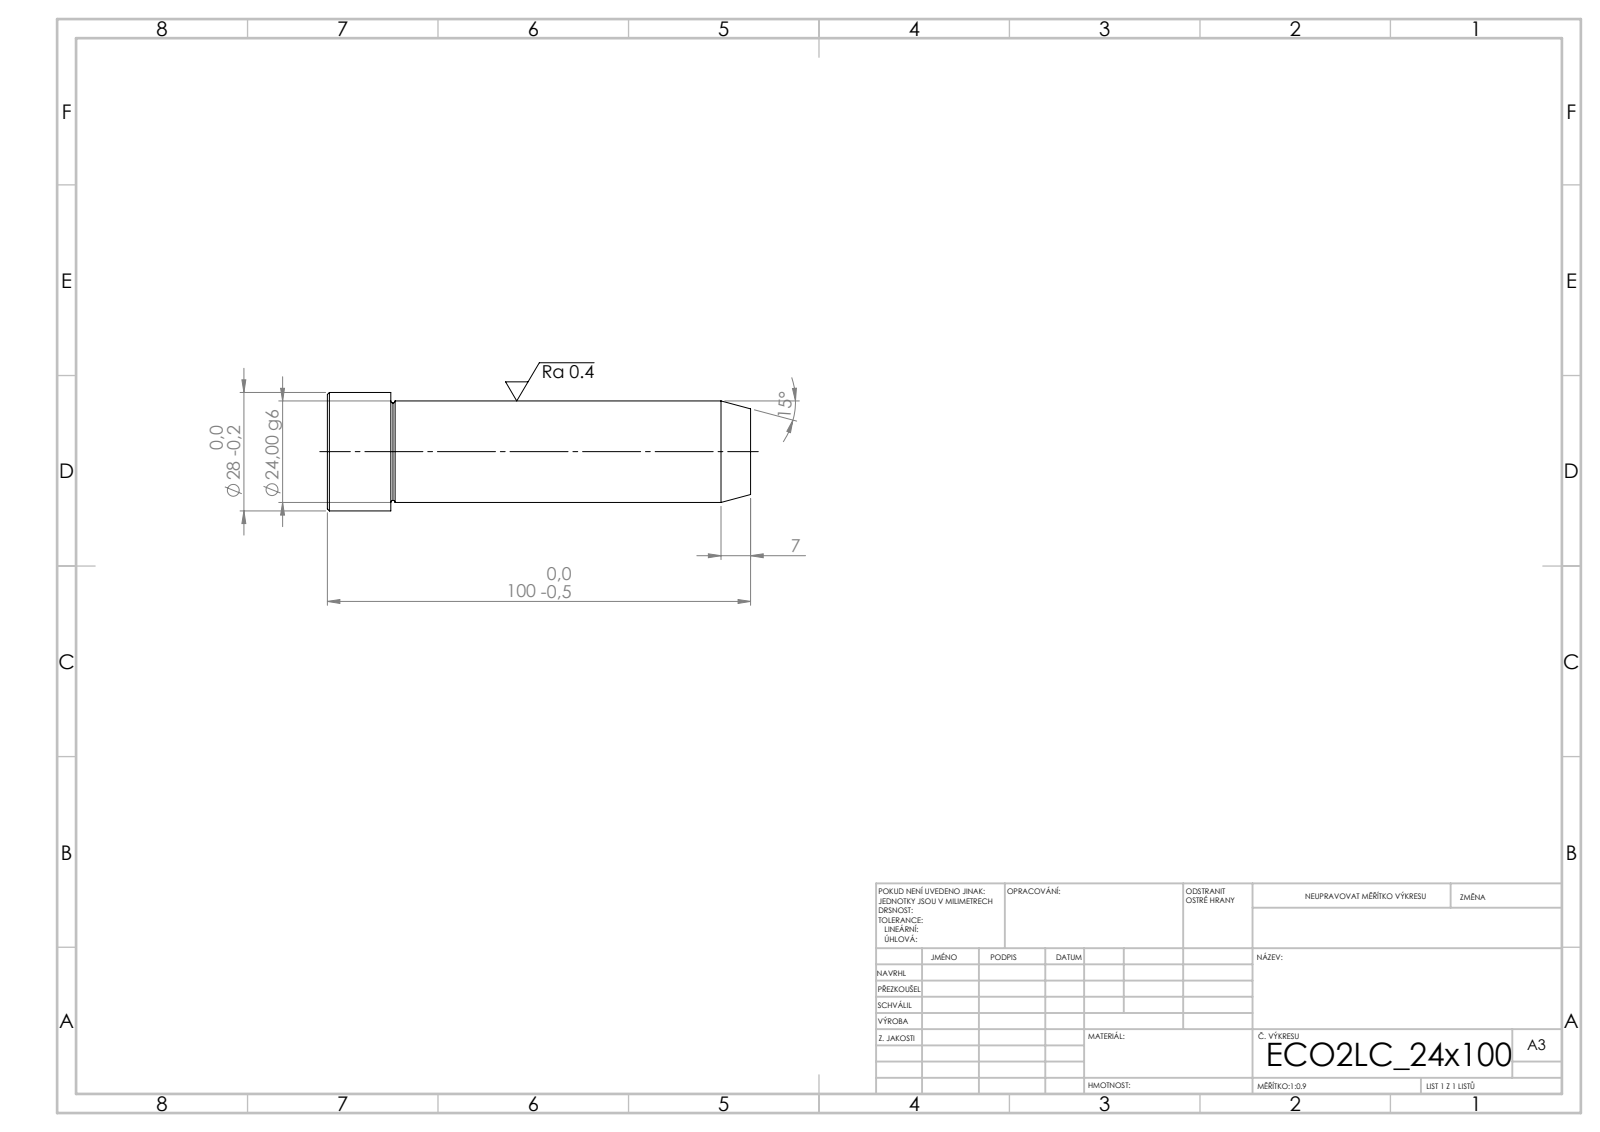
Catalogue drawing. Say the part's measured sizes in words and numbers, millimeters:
Its 3-D file was written by "SolidWorks 2019 (CONFIG_CONTROL_DESIGN)". It is 1 solid with 15 faces: 3 planar, 4 cylindrical and 8 other. Overall it measures 100 by 28 by 28 millimeters. Its volume is 47 180 cubic millimeters and its surface area 8 819 square millimeters. Round bosses or shafts: 1 of diameter 28, 1 of diameter 24. The main face-to-face distances are 100, 85, 15.
